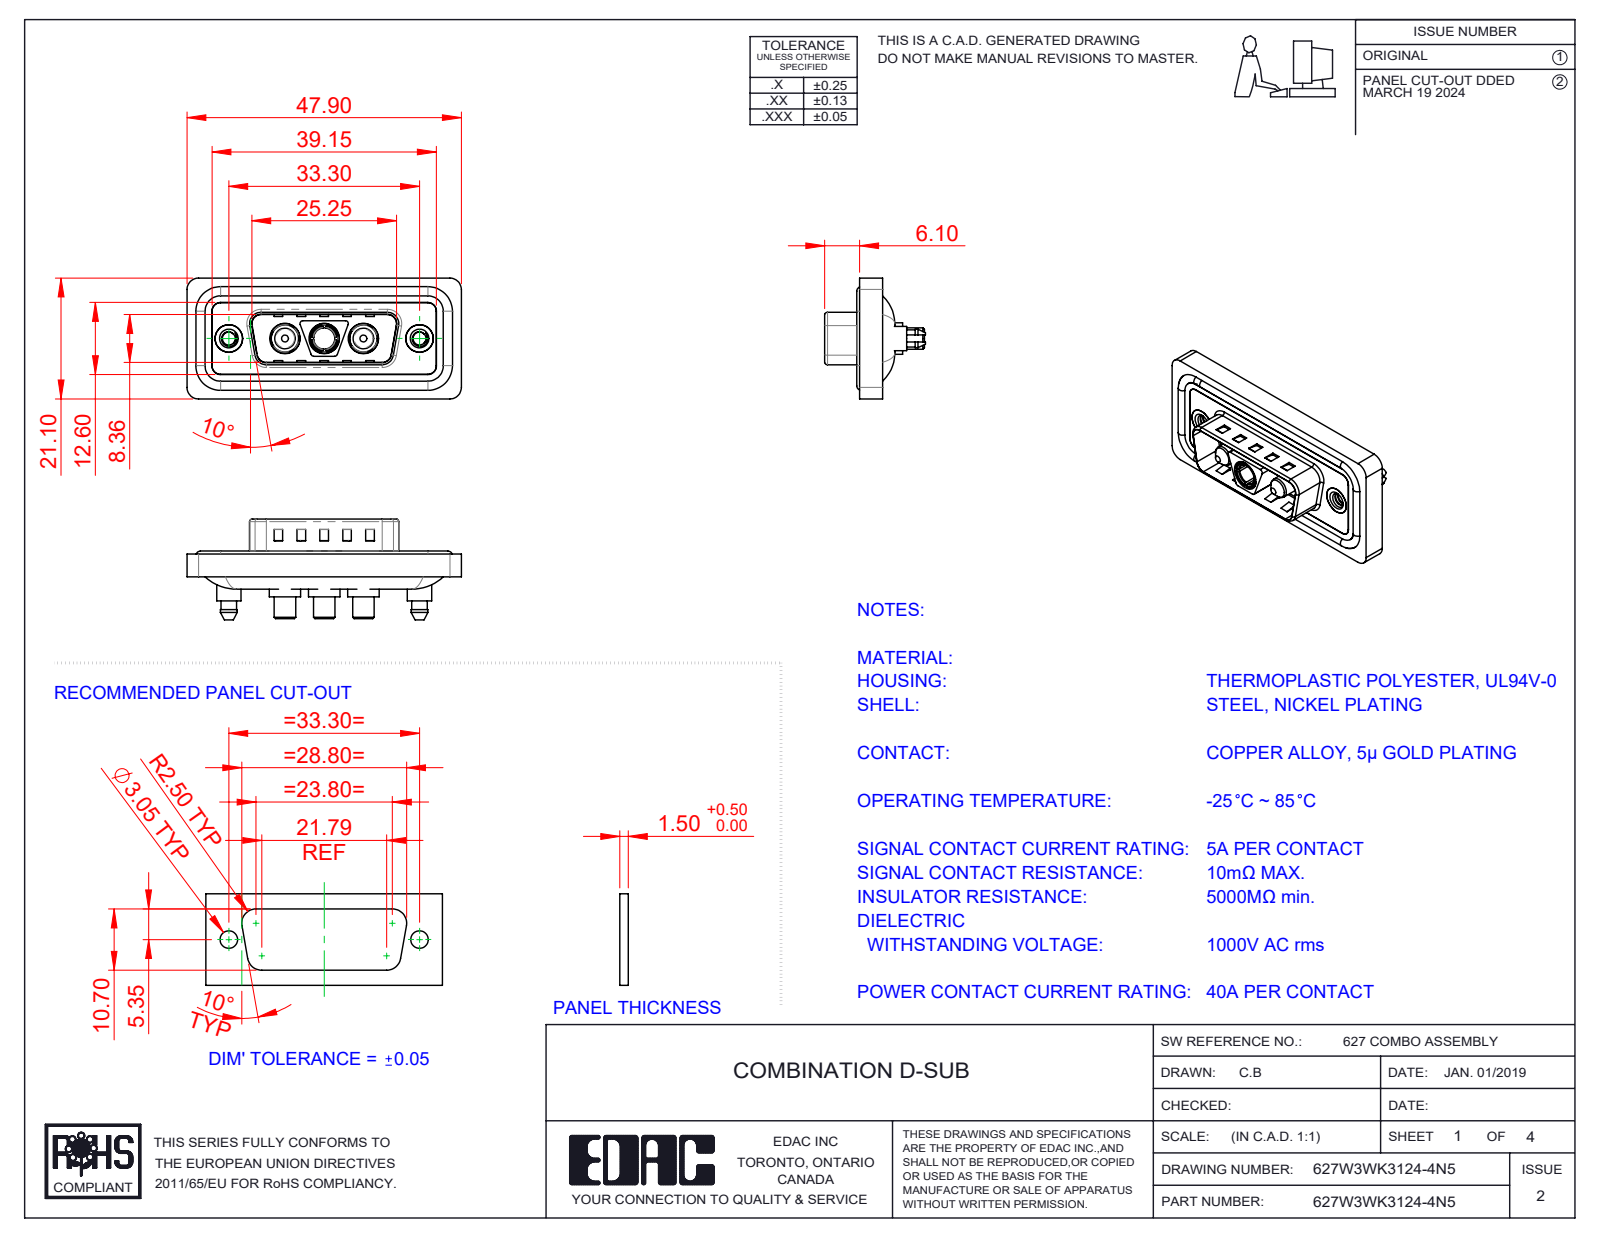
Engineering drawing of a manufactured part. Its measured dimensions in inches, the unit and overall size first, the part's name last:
Units: inches
Overall size (bounding box): 1.886 × 0.831 × 0.693
Round holes (diameter × count): ⌀0.191 ×3, ⌀0.209 ×3, ⌀0.089 ×2, ⌀0.157 ×2, ⌀0.189 ×2, ⌀0.197 ×2, ⌀0.146 ×1
Round bosses / shafts (diameter × count): ⌀0.063 ×4, ⌀0.217 ×3, ⌀0.205 ×3, ⌀0.187 ×3, ⌀0.148 ×3, ⌀0.213 ×2, ⌀0.193 ×2, ⌀0.167 ×2
Partial cylindrical surfaces — rounded edges, fillets, slot ends (radius × count): R0.059 ×28, R0.079 ×20, R0.02 ×12, R0.063 ×10, R0.01 ×4, R0.024 ×4, R0.026 ×4, R0.035 ×4
Main face-to-face distances: 0.016, 0.043, 0.059, 0.122, 0.02, 0.063, 0.114, 0.157, 0.028, 0.032
Hole centre spacings: 0.27, 0.386, 0.656, 0.925, 0.539, 1.311
Volume: 0.359 in³ · Surface area: 14.71 in²
Bodies: 13 solids, 659 faces (247 planar, 282 cylindrical, 130 other)
Part name (STEP PRODUCT): Power Pin_40A S; 627Combo Shell Rear_15 Contacts; 627W3WK3124-4N5; 627Combo Shell Front_15 Contacts (+4 more)
STEP written by: SolidWorks 2023 (CONFIG_CONTROL_DESIGN)
